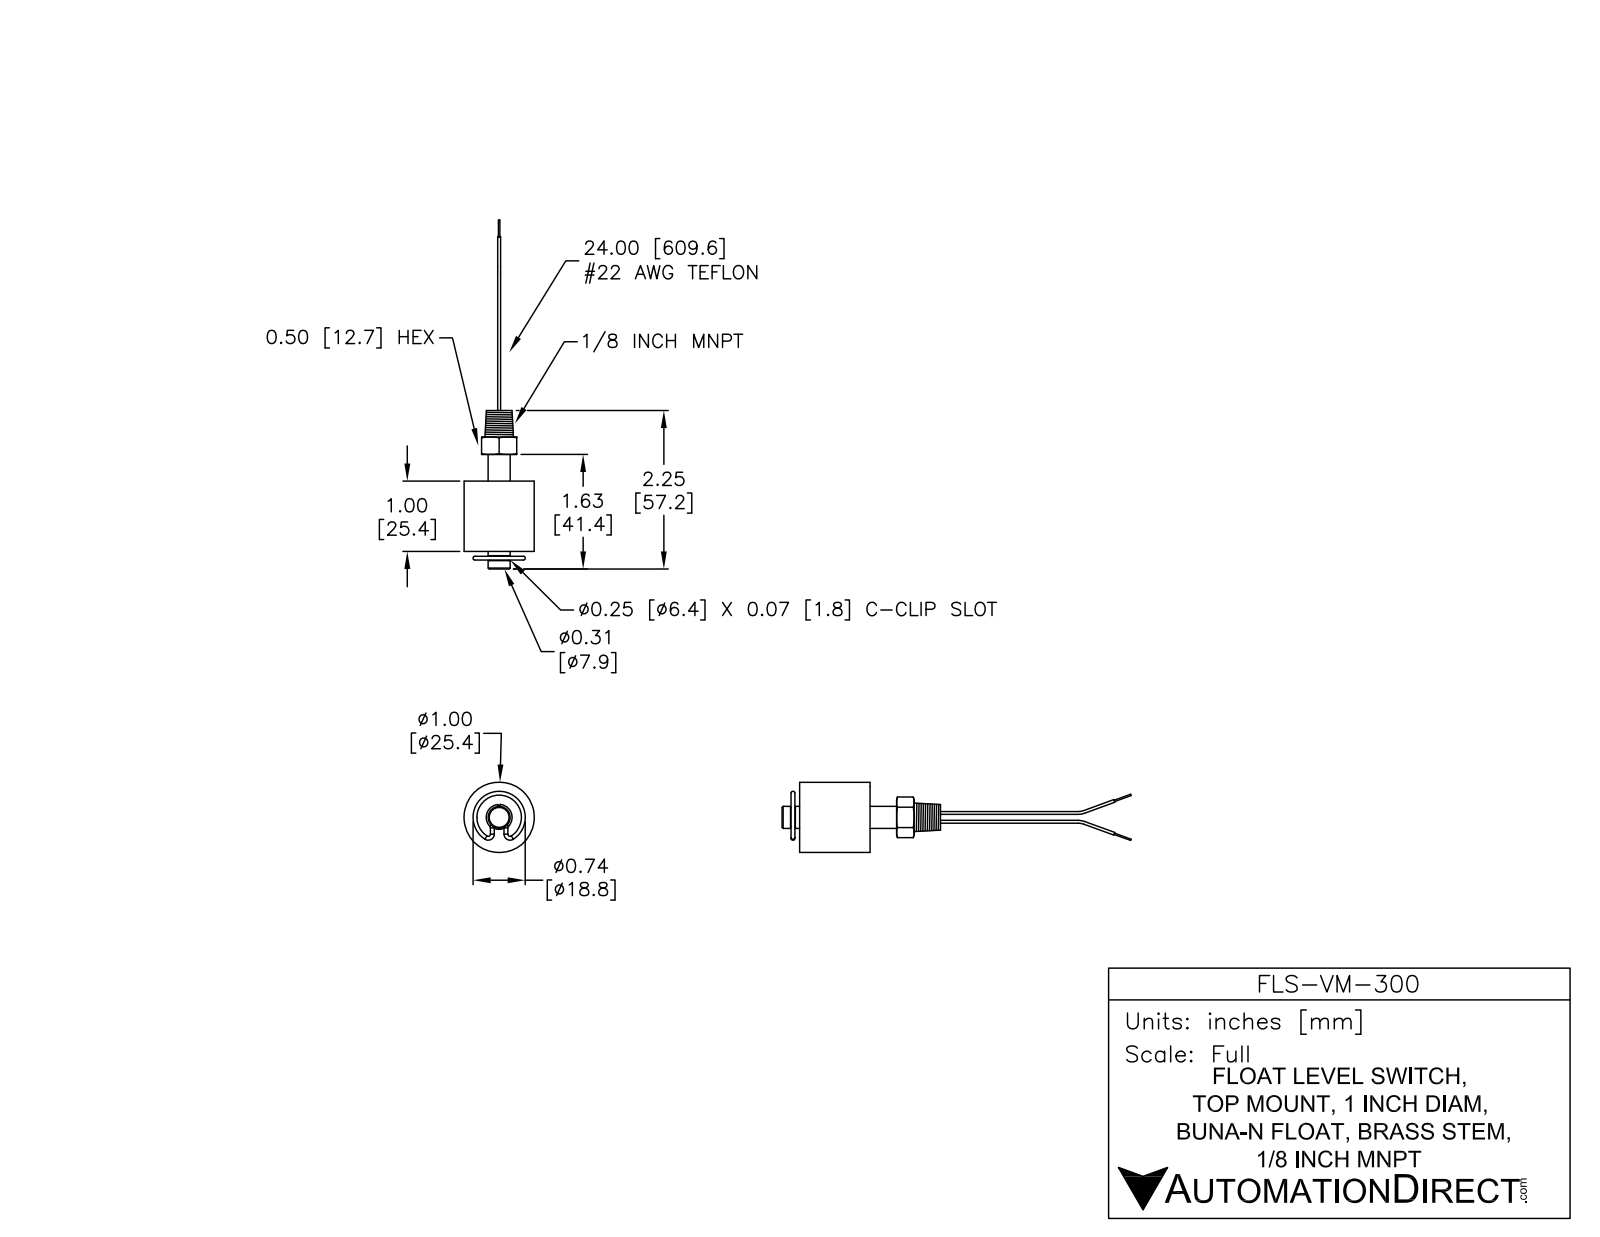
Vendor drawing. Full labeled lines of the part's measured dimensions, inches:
Part name (STEP PRODUCT): FLS-VM-300
STEP written by: SolidWorks 2013 (AUTOMOTIVE_DESIGN)
Units: inches
Bodies: 6 solids, 71 faces (23 planar, 22 cylindrical, 26 other)
Overall size (bounding box): 4.984 × 1 × 1
Volume: 0.921 in³ · Surface area: 10.3 in²
Round holes (diameter × count): ⌀0.38 ×1
Round bosses / shafts (diameter × count): ⌀0.04 ×4, ⌀0.02 ×2, ⌀1 ×1, ⌀0.313 ×1, ⌀0.313 ×1, ⌀0.25 ×1
Main face-to-face distances: 1, 1.365, 0.365, 0.25, 1.615, 0.615, 0.145, 1.145, 1.51, 1.76
